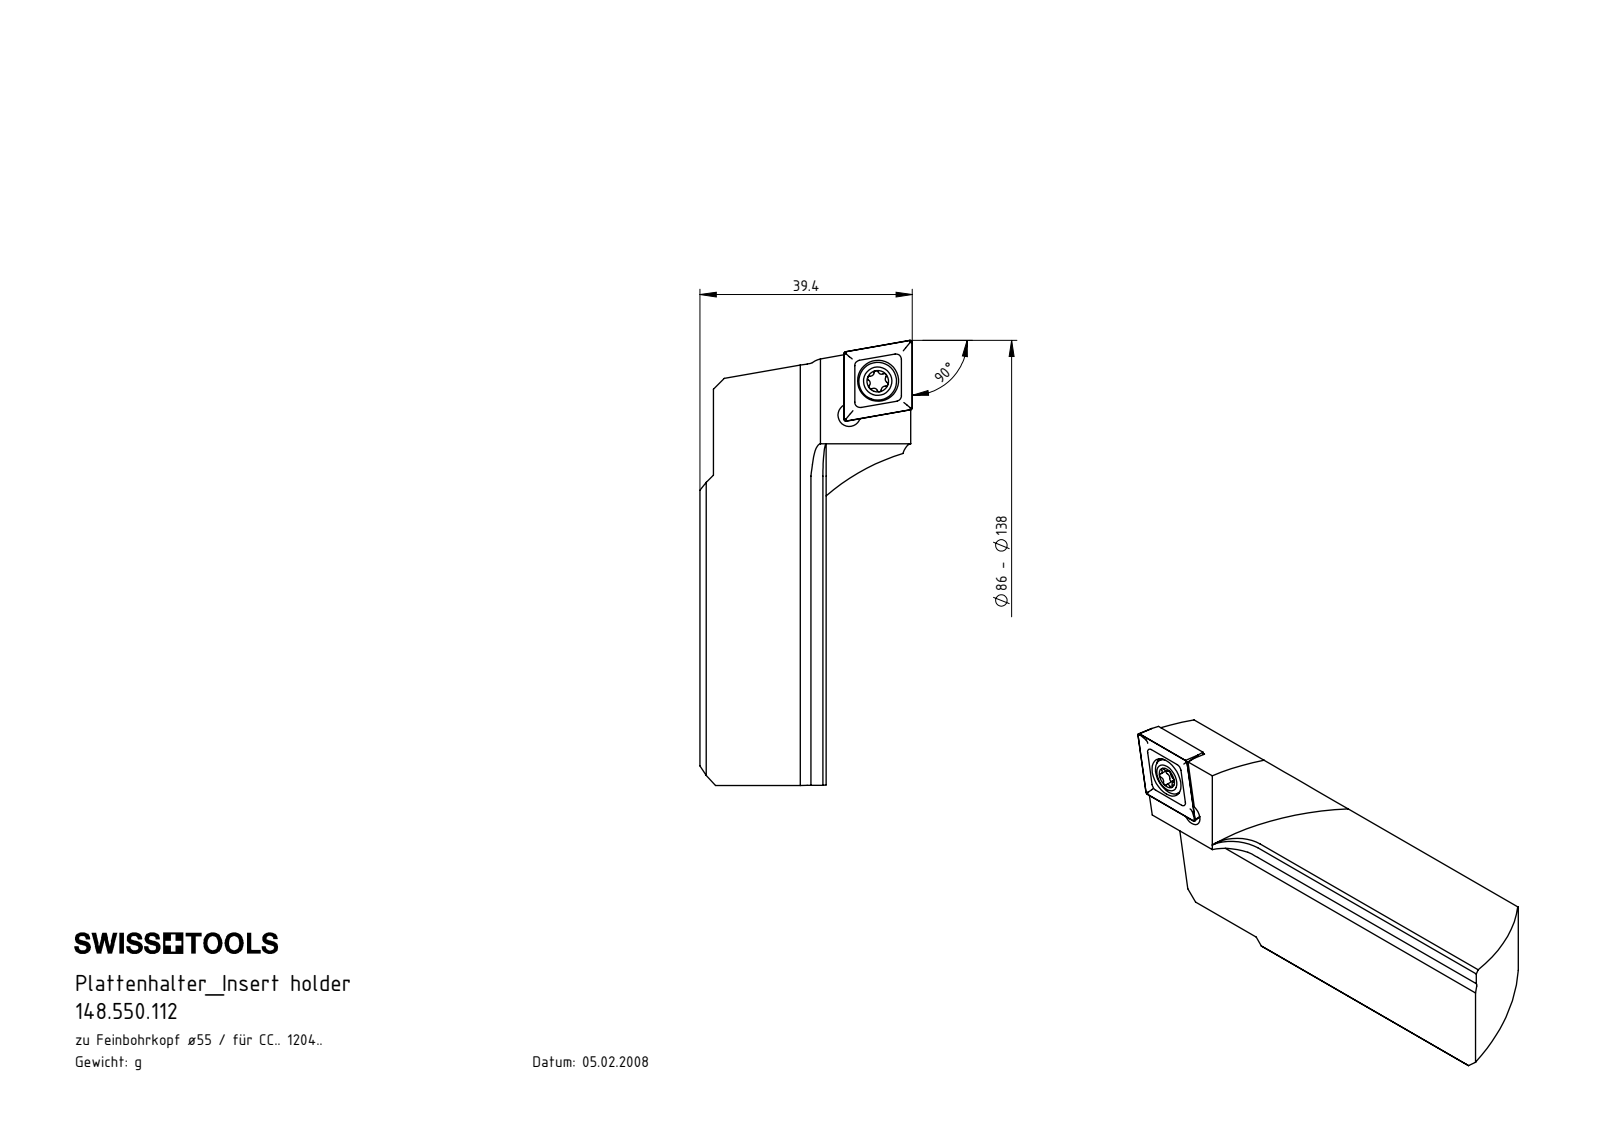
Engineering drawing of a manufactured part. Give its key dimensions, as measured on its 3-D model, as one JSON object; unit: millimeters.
{"part_name": "WCC-ER2.001.010_A; F00-WCC.086.001_C; CCMT120404; 148.550.112", "step_written_by": "SolidWorks 2017 (CONFIG_CONTROL_DESIGN)", "units": "millimeters", "bodies": {"solids": 3, "faces": 379, "planar": 226, "cylindrical": 40, "other": 113}, "overall_size": [82.58, 39.4, 27.35], "volume_mm3": 33749, "surface_area_mm2": 9364, "round_holes": [[4.2, 2], [5.5, 1], [7.6, 1]], "round_bosses_or_shafts": [[7, 1], [5, 1]], "partial_cylinders_radius": [[0.2, 8], [0.39, 6], [0.69, 3], [0.69, 3], [40, 3], [0.8, 1], [6, 1]], "face_to_face_distances": [2.38, 21.3, 4.76, 7.14, 9.52, 4.77, 7.15, 9.53, 11.91, 14.29], "hole_center_spacings": [8.21, 8.33]}
